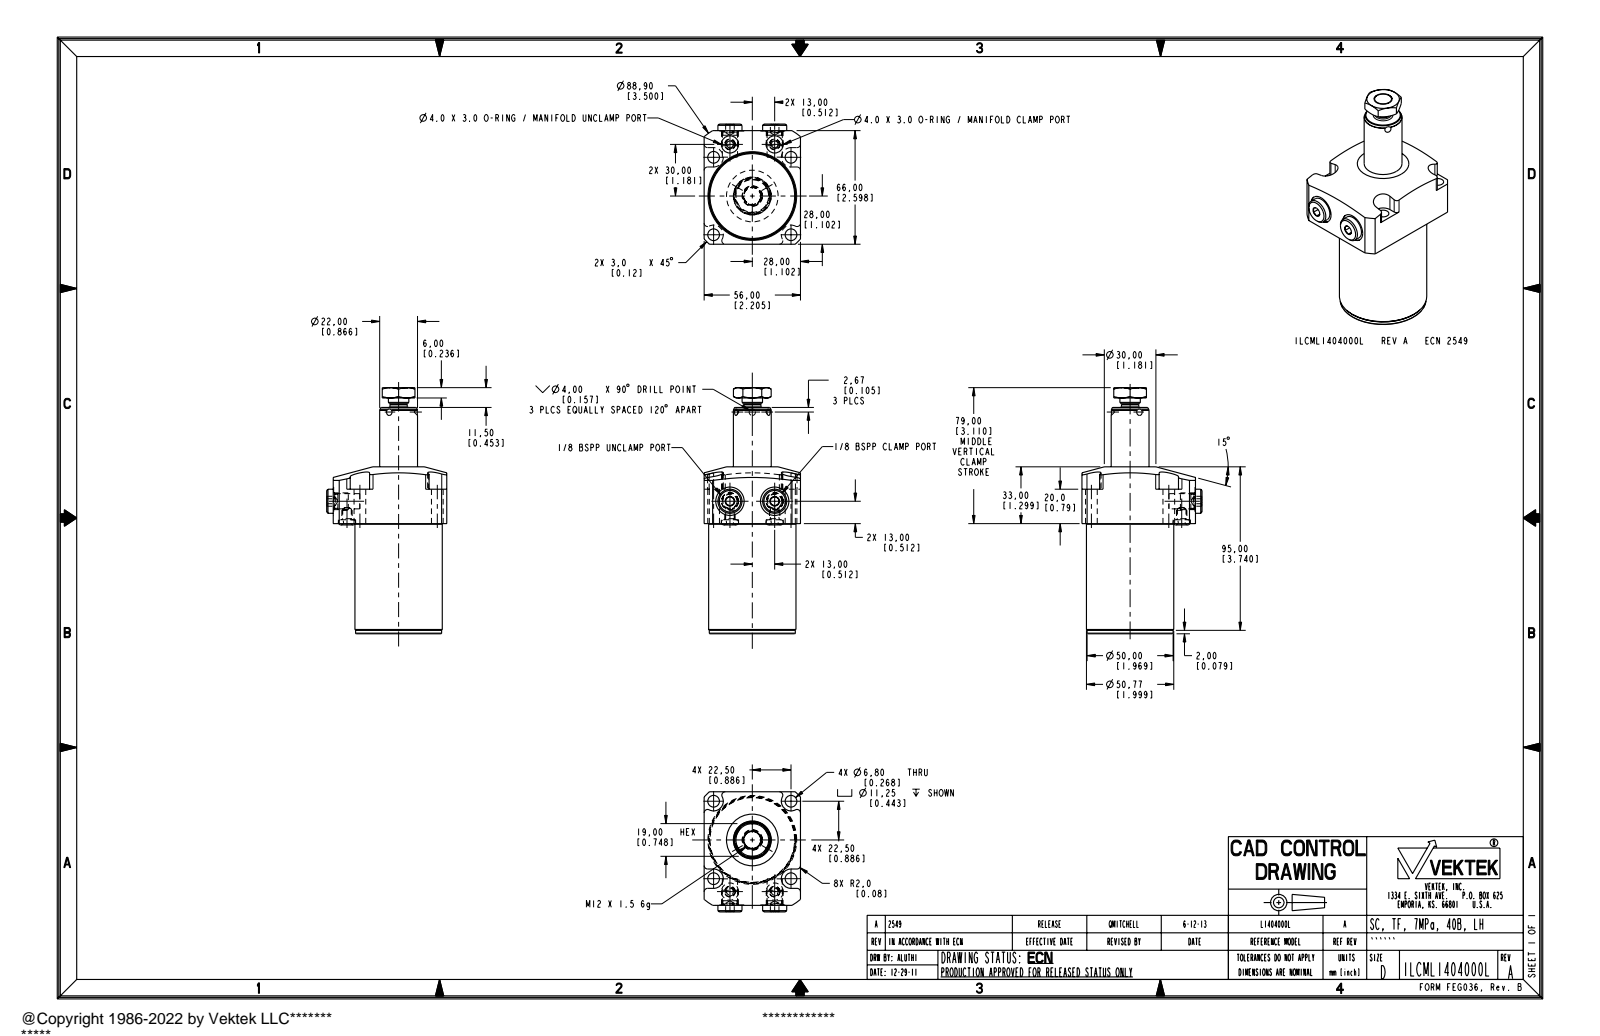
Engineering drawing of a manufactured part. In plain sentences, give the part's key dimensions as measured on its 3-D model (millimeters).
The part is named "ILCML1404000L". Its 3-D file was written by "PRO/ENGINEER BY PARAMETRIC TECHNOLOGY CORPORATION, 2007460 (AUTOMOTIVE_DESIGN_CC2)". It is 3 solids with 215 faces: 68 planar, 70 cylindrical and 77 other. Overall it measures 143 by 69.81 by 56 millimeters. Its volume is 248 946 cubic millimeters and its surface area 32 477 square millimeters. Round holes: 4 of diameter 5, 4 of diameter 6.8, 2 of diameter 8.84, 2 of diameter 10, 2 of diameter 16.5, 1 of diameter 10.5. Round bosses or shafts: 2 of diameter 14, 2 of diameter 9.73, 2 of diameter 8.25, 2 of diameter 6, 1 of diameter 50.77, 1 of diameter 50, 1 of diameter 22, 1 of diameter 11.87. Partial cylindrical surfaces (rounded edges, fillets, slot ends): 8 of radius 2, 4 of radius 5.62, 1 of radius 44.45. The main face-to-face distances are 56, 64, 66, 13, 97, 33, 84, 20, 143, 79. The hole center spacings are 31.82, 45, 12.1, 26, 32.7, 36.28, 53.35, 63.38.
